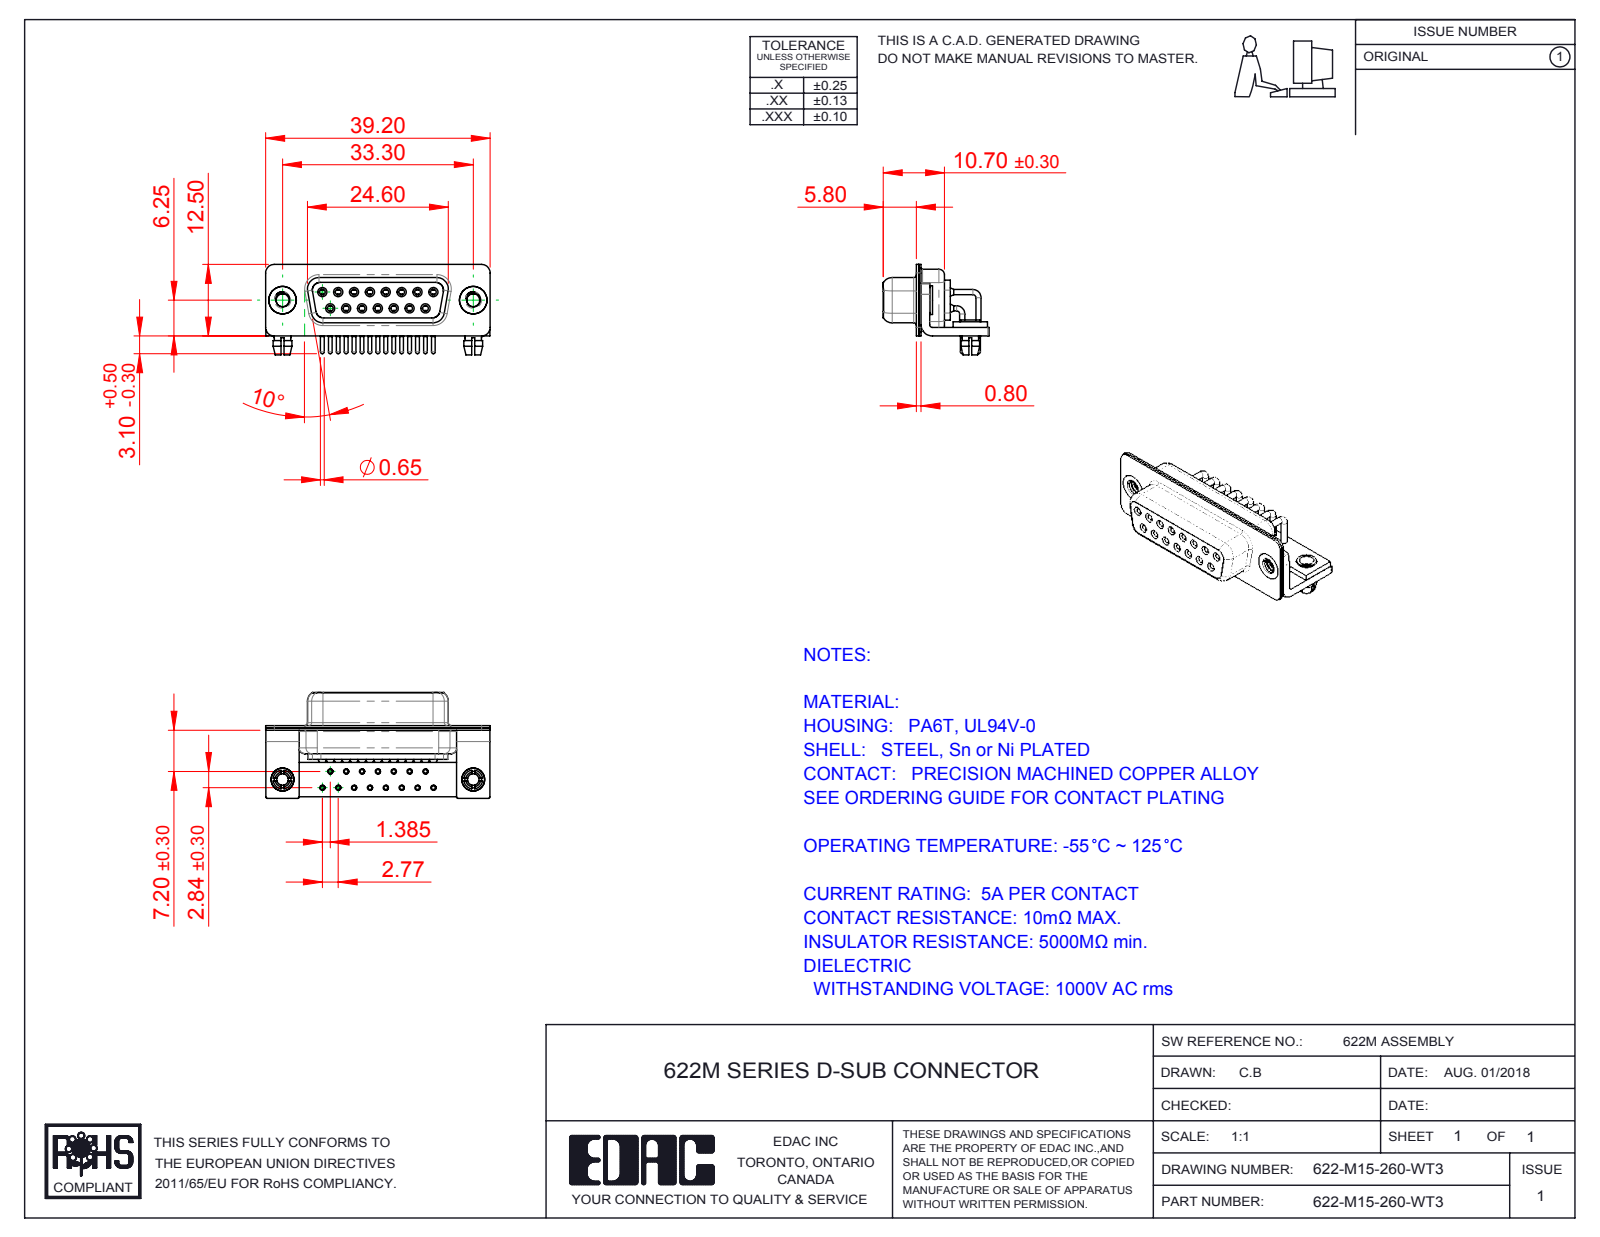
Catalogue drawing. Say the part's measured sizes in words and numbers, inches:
The part is named "622M Board Lock; 622M Stabilizer Board_15 Contacts; 622M Stabilizer Bracket; 622M 4-40 Threaded Rivet_Stabilizer (+6 more)". Its 3-D file was written by "SolidWorks 2016 (CONFIG_CONTROL_DESIGN)". It is 25 solids with 1246 faces: 366 planar, 566 cylindrical and 314 other. Overall it measures 1.543 by 0.728 by 0.622 inches. Its volume is 0.184 cubic inches and its surface area 12.01 square inches. Round holes: 17 of diameter 0.079, 15 of diameter 0.035, 15 of diameter 0.039, 15 of diameter 0.043, 15 of diameter 0.067, 15 of diameter 0.071, 2 of diameter 0.089, 2 of diameter 0.098, 2 of diameter 0.126, 2 of diameter 0.157, 2 of diameter 0.189. Round bosses or shafts: 22 of diameter 0.035, 15 of diameter 0.063, 15 of diameter 0.059, 15 of diameter 0.026, 2 of diameter 0.197, 2 of diameter 0.193, 2 of diameter 0.157, 2 of diameter 0.134. Partial cylindrical surfaces (rounded edges, fillets, slot ends): 16 of radius 0.01, 16 of radius 0.059, 13 of radius 0.079, 8 of radius 0.053, 8 of radius 0.063, 5 of radius 0.02, 4 of radius 0.024, 4 of radius 0.026. The main face-to-face distances are 0.016, 0.031, 0.091, 0.075, 0.368, 0.059, 0.039, 0.057, 0.352, 0.033. The hole center spacings are 0.124, 0.109, 0.218, 0.327, 0.436, 0.198, 0.198, 0.294.
